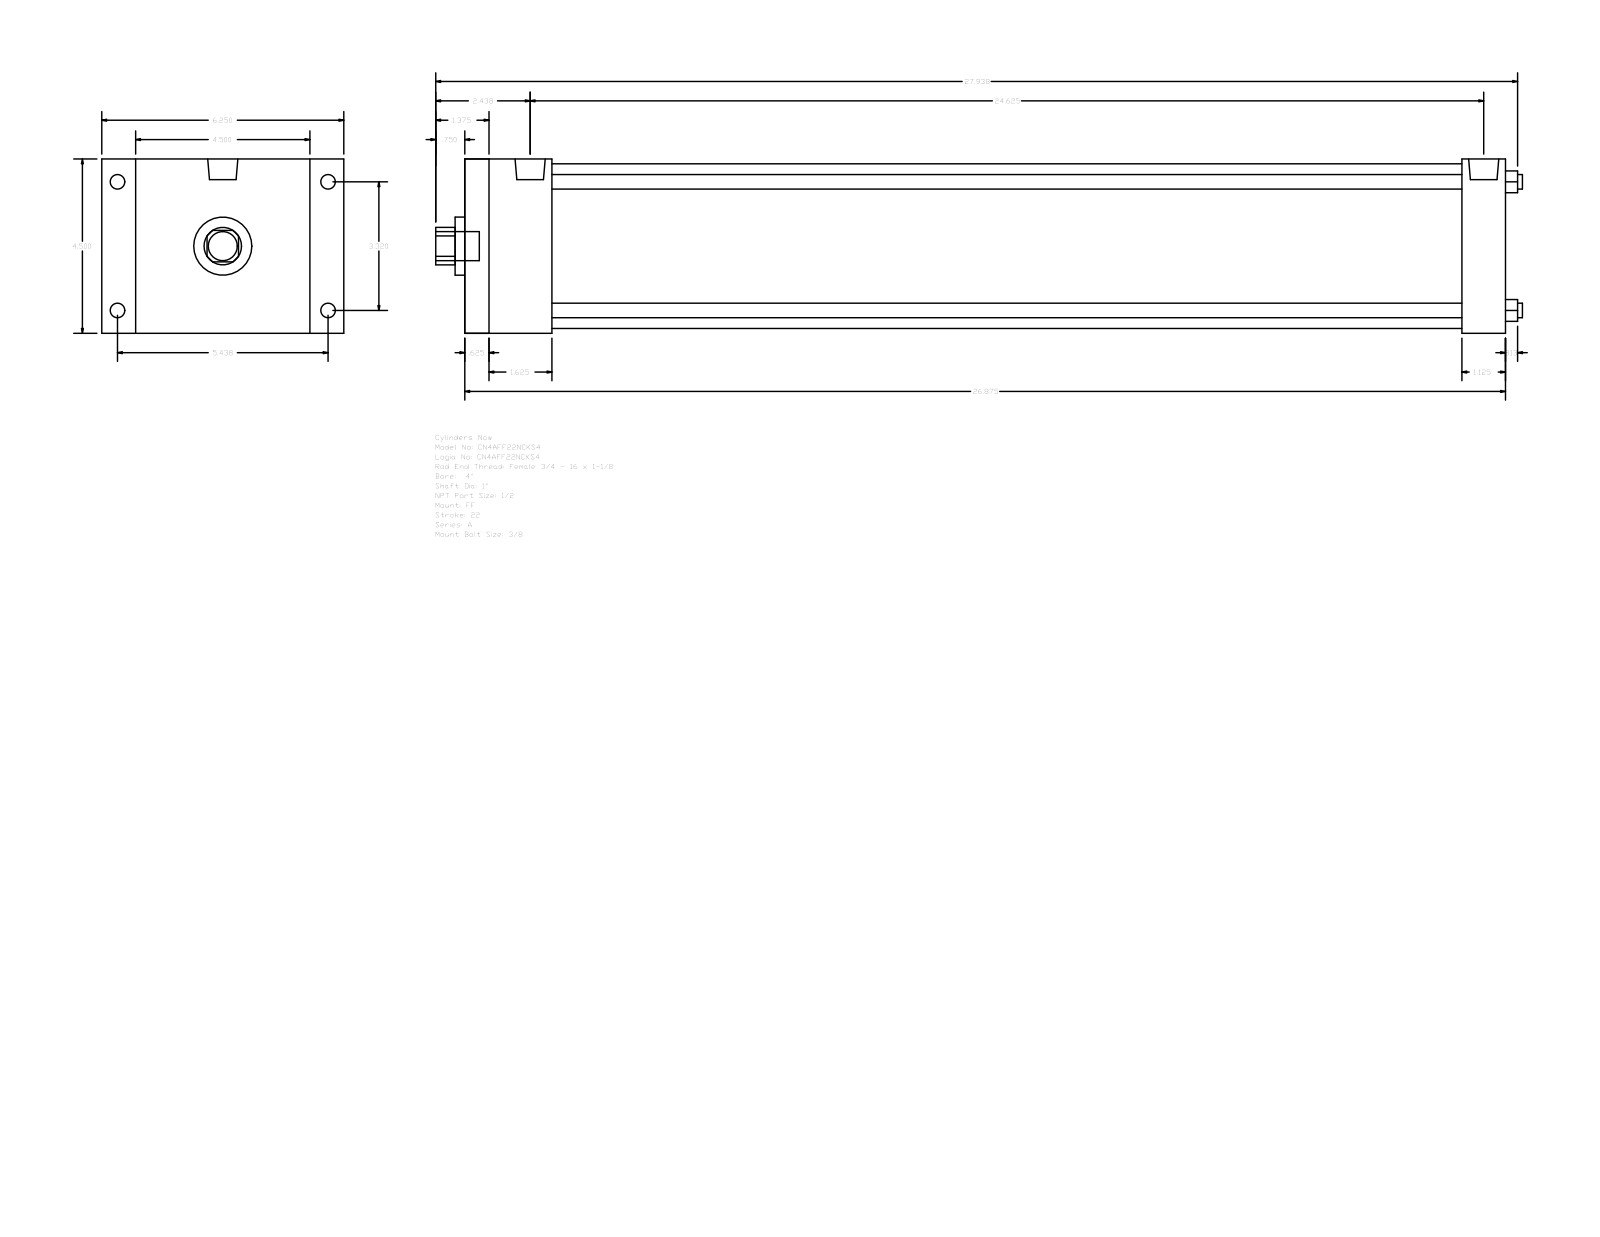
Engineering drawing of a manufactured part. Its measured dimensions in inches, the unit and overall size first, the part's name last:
Units: inches
Overall size (bounding box): 28.063 × 6.25 × 4.5
Round holes (diameter × count): ⌀0.375 ×4, ⌀1 ×1, ⌀1.5 ×1, ⌀4.25 ×1
Round bosses / shafts (diameter × count): ⌀0.375 ×4, ⌀0.344 ×4, ⌀0.778 ×2, ⌀0.75 ×1
Partial cylindrical surfaces — rounded edges, fillets, slot ends (radius × count): R0.484 ×1
Main face-to-face distances: 4.5, 26.875, 0.625, 26.25, 1.125, 0.875, 5.375, 25.75, 25.125, 2.25
Hole centre spacings: 2.347, 3.32, 4.695
Bodies: 0 solids, 92 faces (64 planar, 28 cylindrical, 0 other)
Part name (STEP PRODUCT): A_FF__0400_1
STEP written by: GSSL Pune (CONFIG_CONTROL_DESIGN)
